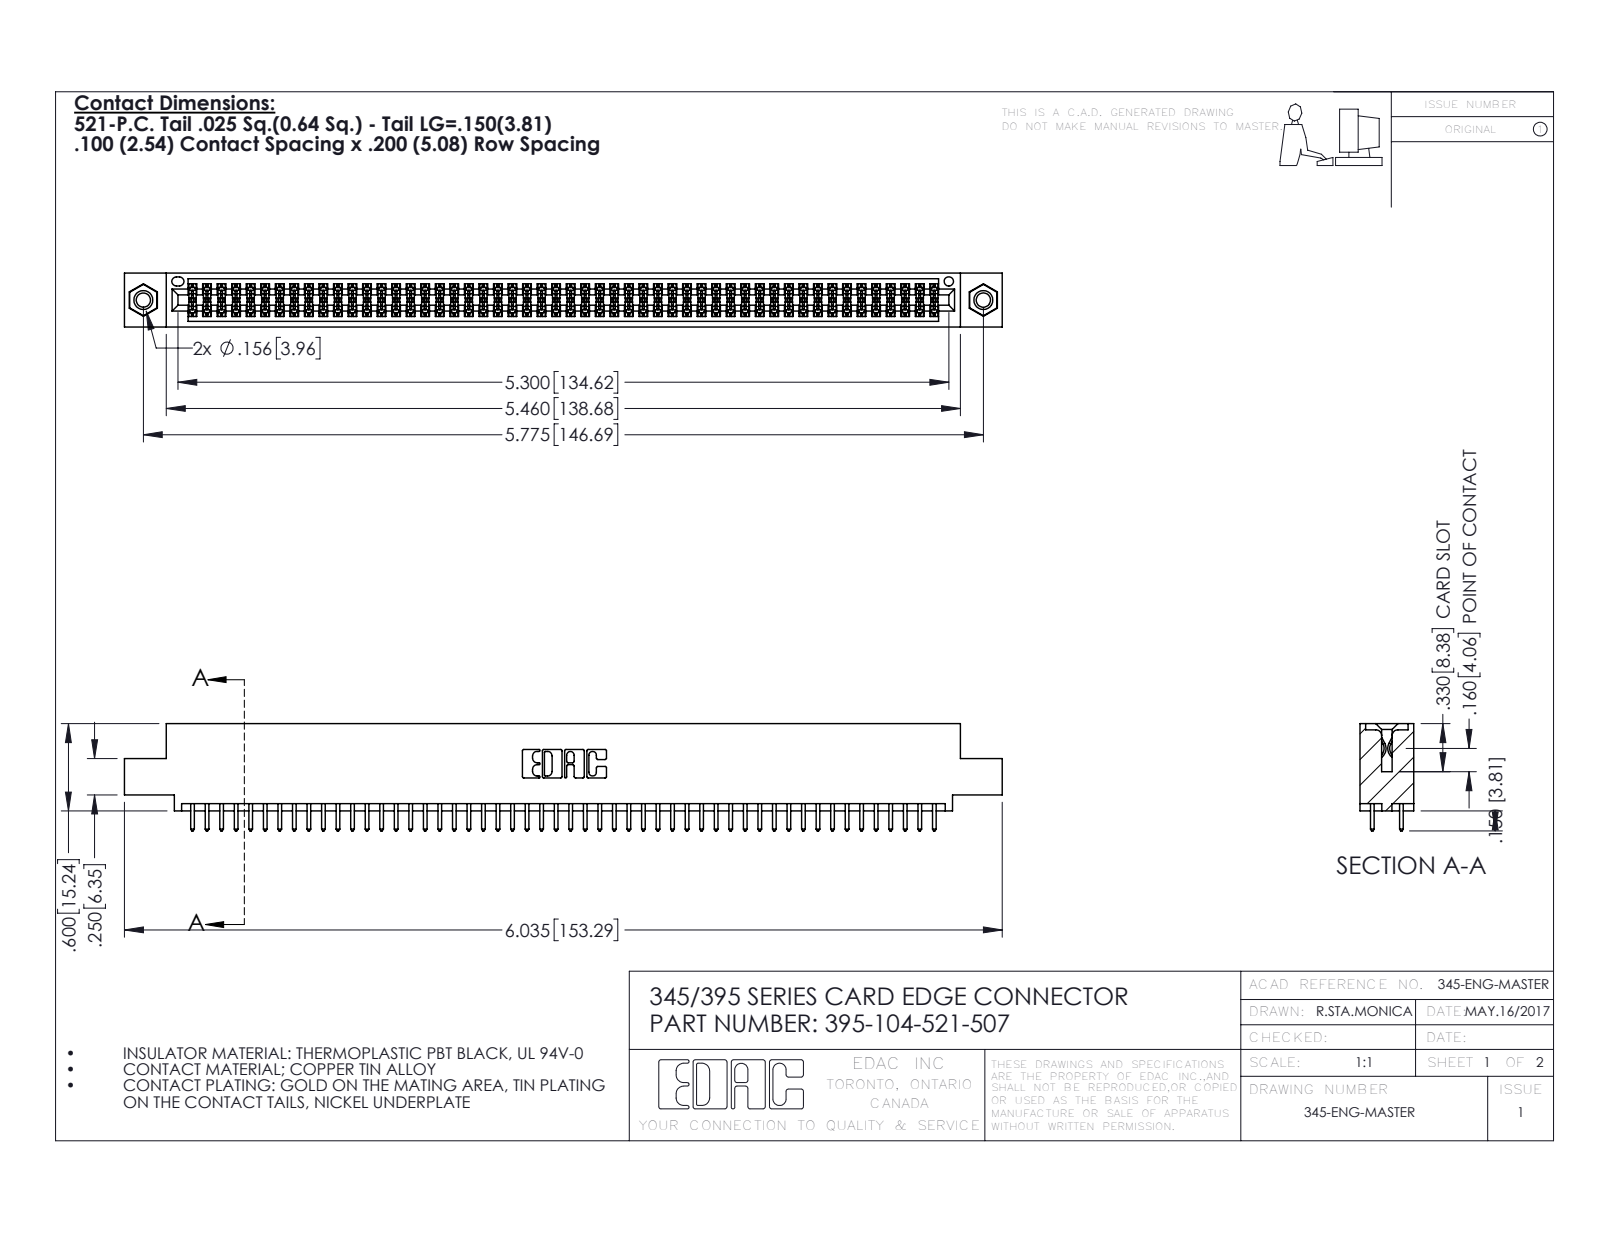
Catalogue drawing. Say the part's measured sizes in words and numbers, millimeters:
The part is named "395-104-521-507; 345 Part_0.110 Offset - 0.156 Dia-TI; 345-250-001_345-250-005-103; 345-292-001_345-293-121". Its 3-D file was written by "SolidWorks 2016 (CONFIG_CONTROL_DESIGN)". It is 107 solids with 5390 faces: 3548 planar, 1826 cylindrical and 16 other. Overall it measures 153.3 by 18.7 by 9.4 millimeters. Its volume is 14 800 cubic millimeters and its surface area 21 990 square millimeters. Round holes: 2 of diameter 2.5, 2 of diameter 3.2, 2 of diameter 4, 1 of diameter 1.6. Round bosses or shafts: 2 of diameter 3.9. Partial cylindrical surfaces (rounded edges, fillets, slot ends): 156 of radius 0.2, 104 of radius 0.3, 22 of radius 0.3, 6 of radius 0.2, 6 of radius 0.8, 3 of radius 0.7, 2 of radius 0.4, 2 of radius 0.5. The main face-to-face distances are 1.8, 7.6, 5.1, 9.4, 2.5, 6.9, 0.6, 5.7, 4.4, 3.8. The hole center spacings are 6.9, 140.7, 146.7.
